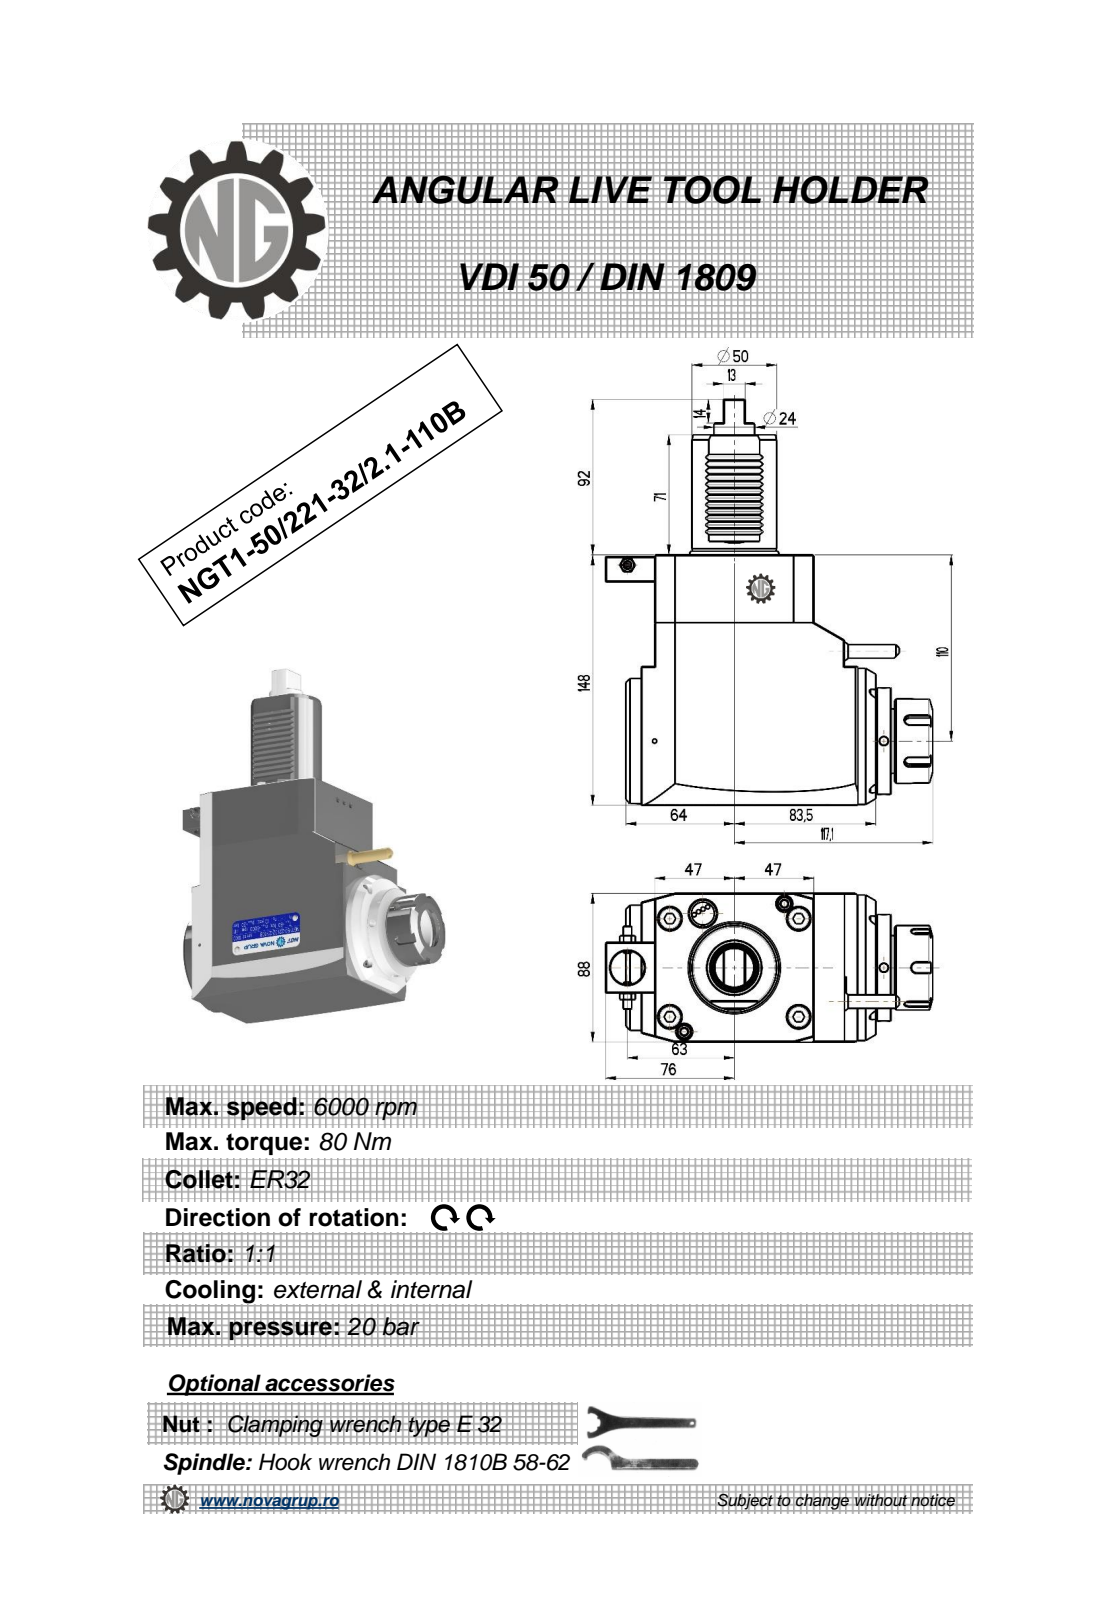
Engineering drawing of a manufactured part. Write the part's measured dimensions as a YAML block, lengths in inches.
part_name: "NGT1_50_221_32_1_1_110B"
step_written_by: "PRO/ENGINEER BY PARAMETRIC TECHNOLOGY CORPORATION, 2010280 (CONFIG_CONTROL_DESIGN)"
units: inches
bodies: {solids: 1, faces: 417, planar: 198, cylindrical: 95, other: 124}
overall_size: [9.449, 7.602, 3.465]
volume: 109.8
surface_area: 172.7
round_holes:
  - {diameter: 0.197, count: 3}
  - {diameter: 0.15, count: 2}
  - {diameter: 0.157, count: 2}
  - {diameter: 0.118, count: 1}
  - {diameter: 0.374, count: 1}
  - {diameter: 0.787, count: 1}
  - {diameter: 1.063, count: 1}
round_bosses_or_shafts:
  - {diameter: 1.969, count: 2}
  - {diameter: 3.386, count: 1}
  - {diameter: 2.913, count: 1}
  - {diameter: 2.48, count: 1}
  - {diameter: 1.988, count: 1}
  - {diameter: 1.614, count: 1}
  - {diameter: 0.945, count: 1}
  - {diameter: 0.394, count: 1}
partial_cylinders:
  - {radius: 0.01, count: 12}
  - {radius: 0.012, count: 12}
  - {radius: 0.008, count: 6}
  - {radius: 0.118, count: 5}
  - {radius: 0.031, count: 2}
  - {radius: 0.098, count: 1}
face_to_face_distances: [3.465, 5.827, 5.807, 0.354, 0.669, 0.315, 3.701, 4.37, 5.138, 1.437]
hole_center_spacings: [0.354, 4.012, 0.709, 1.958, 2.065, 2.225, 2.23, 3.996]
